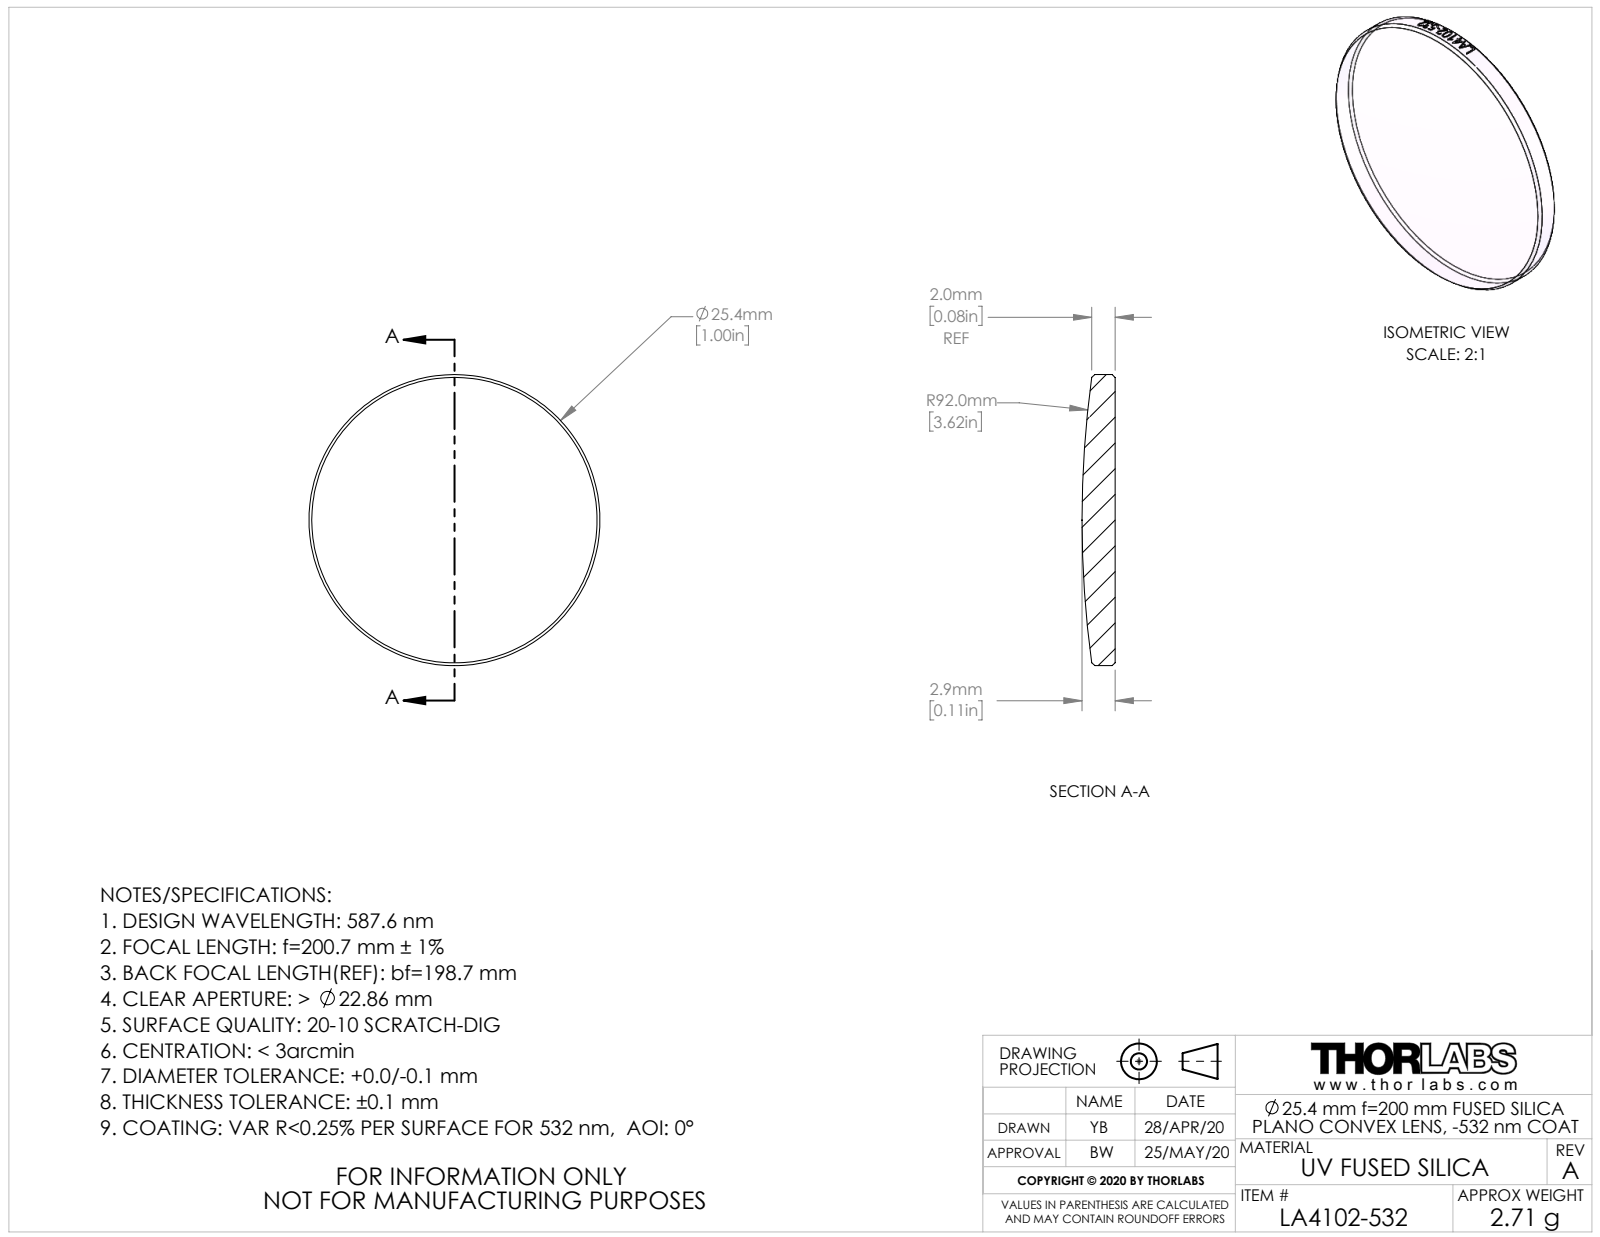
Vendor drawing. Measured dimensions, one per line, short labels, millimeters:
name: CTN015736-E0W
written by: SolidWorks 2018 (AUTOMOTIVE_DESIGN)
unit: mm
bodies: 1 solid, 24 faces (1 planar, 17 cylindrical, 6 other)
size: 25.4 × 25.4 × 2.88
volume: 1 232 mm³; area: 1 154 mm²
bosses: 1× ⌀25.4
